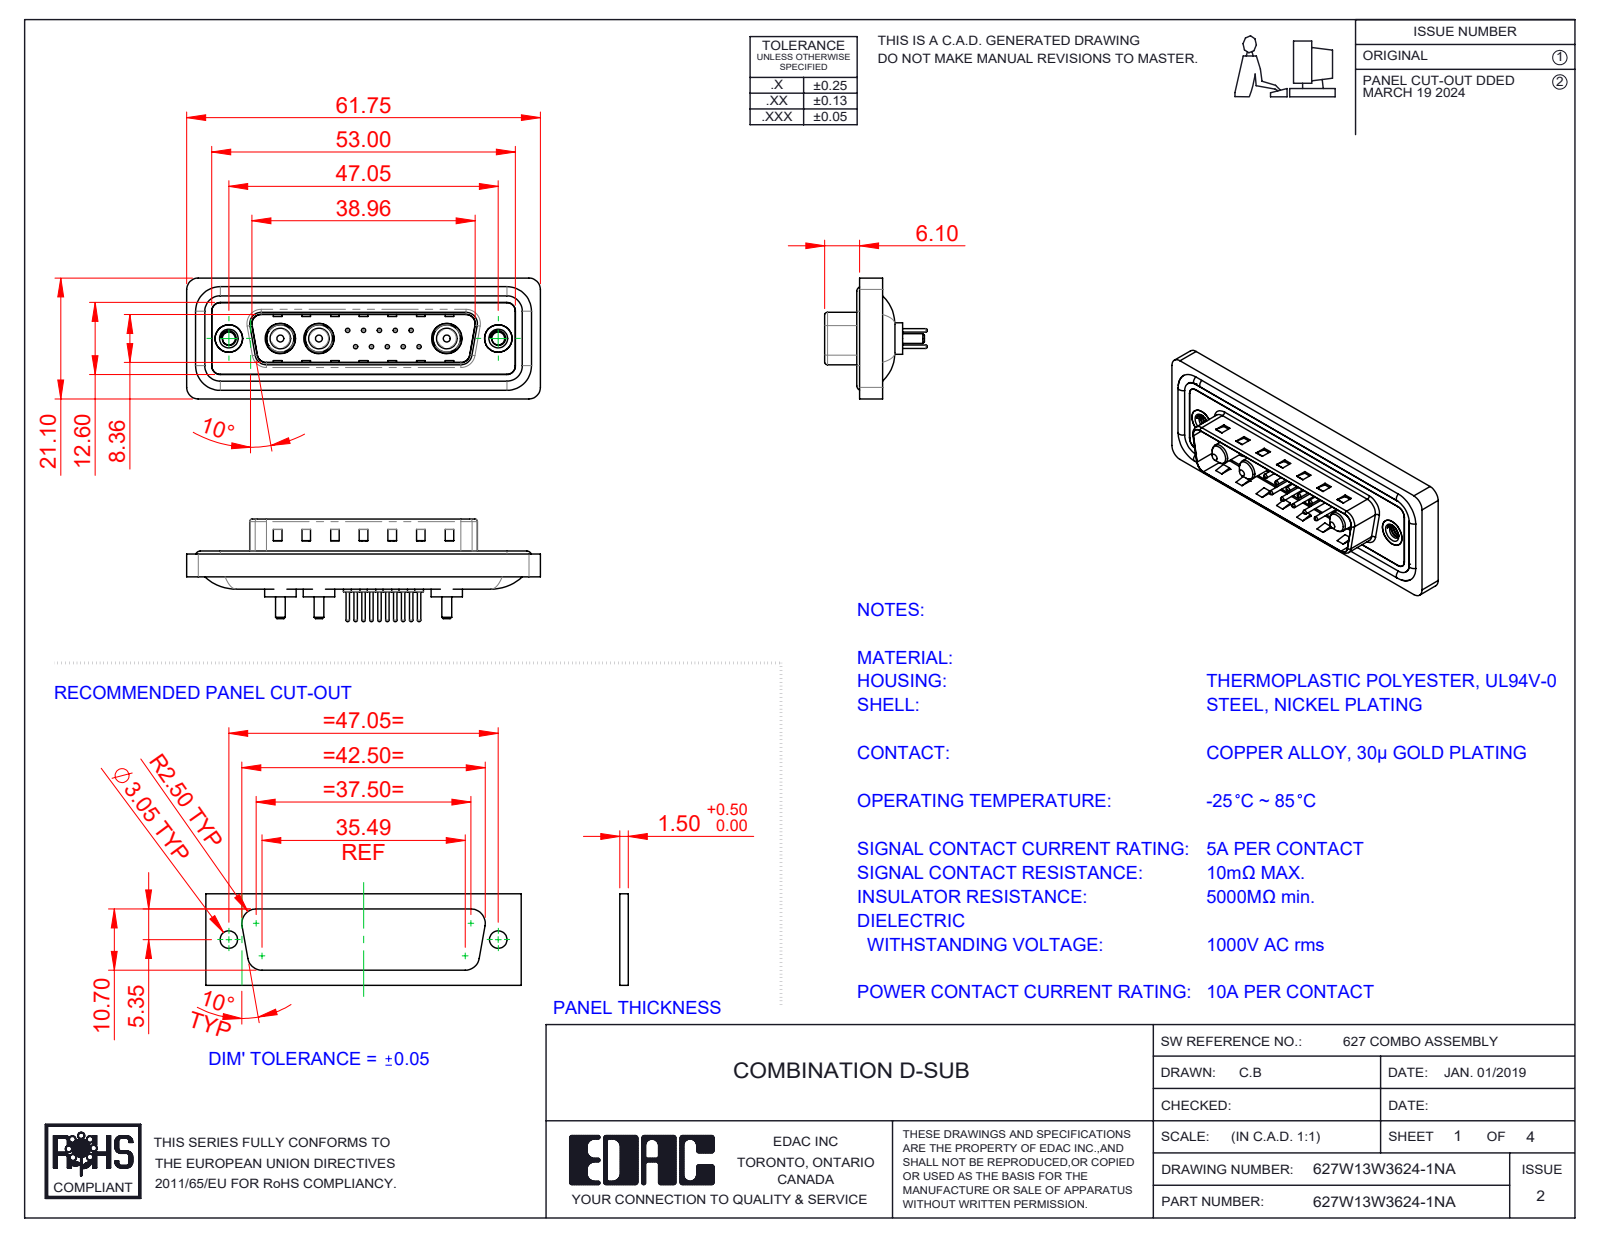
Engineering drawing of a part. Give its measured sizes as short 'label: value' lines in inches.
name: 627W13W3624-1NA; 627Combo Shell Rear_25 Contacts; 627Combo Contact Row 1_24; 627Combo Contact Row 2_24 (+5 more)
written by: SolidWorks 2023 (CONFIG_CONTROL_DESIGN)
unit: in
bodies: 23 solids, 968 faces (309 planar, 387 cylindrical, 272 other)
size: 2.431 × 0.831 × 0.705
volume: 0.445 in³; area: 18.34 in²
holes: 10× ⌀0.03, 10× ⌀0.063, 10× ⌀0.079, 3× ⌀0.191, 3× ⌀0.209, 2× ⌀0.089, 2× ⌀0.157, 2× ⌀0.189, 2× ⌀0.197
bosses: 10× ⌀0.059, 10× ⌀0.024, 4× ⌀0.063, 3× ⌀0.217, 3× ⌀0.205, 3× ⌀0.187, 3× ⌀0.148, 3× ⌀0.142
rounds: 22× R0.059, 18× R0.079, 8× R0.02, 8× R0.063, 4× R0.01, 4× R0.024, 4× R0.026, 4× R0.035
face distances: 0.016, 0.059, 0.043, 0.063, 0.02, 0.122, 0.114, 0.032, 0.377, 0.161
hole spacings: 0.124, 0.109, 0.198, 0.218, 0.295, 0.198, 0.327, 0.398
